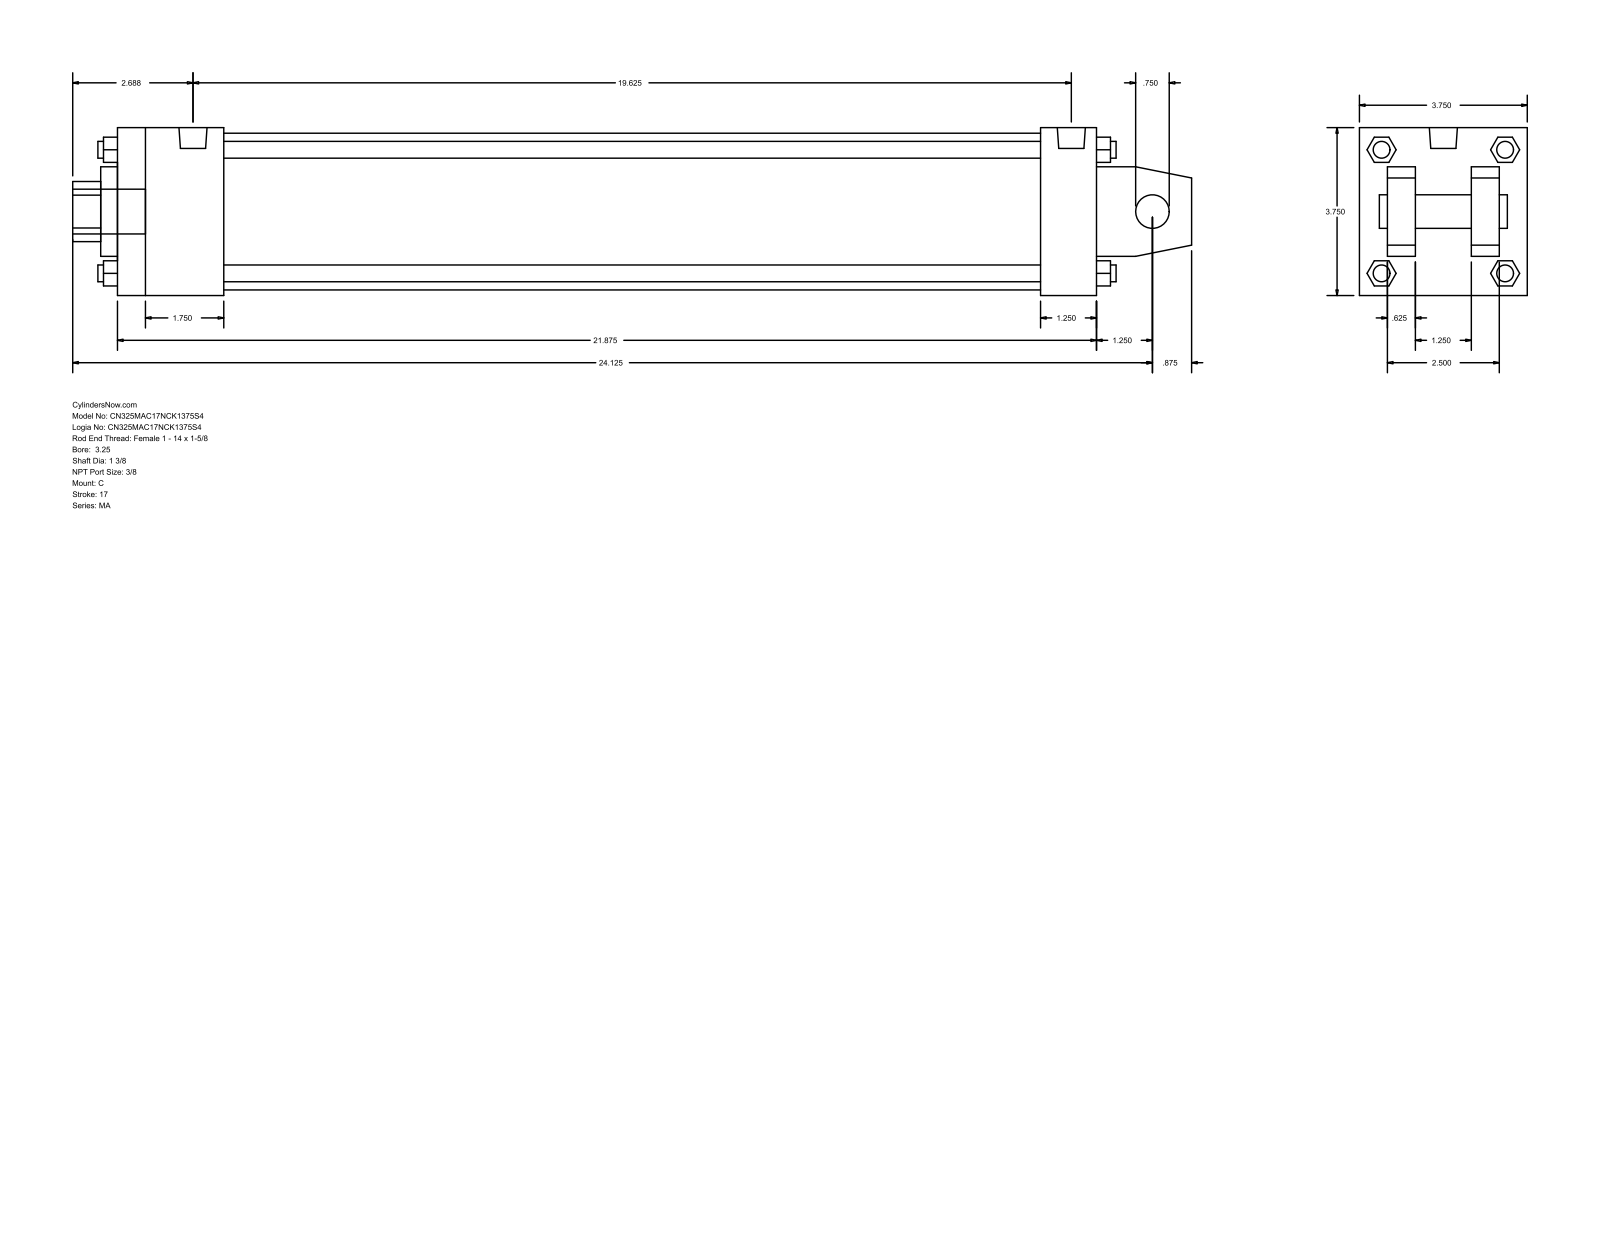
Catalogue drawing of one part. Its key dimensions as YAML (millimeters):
part_name: "MA_C__0325_1.375"
step_written_by: "GSSL Pune (CONFIG_CONTROL_DESIGN)"
units: millimeters
bodies: {solids: 0, faces: 139, planar: 108, cylindrical: 31, other: 0}
overall_size: [635, 95.25, 95.25]
round_holes:
  - {diameter: 19.05, count: 1}
  - {diameter: 34.92, count: 1}
  - {diameter: 50.8, count: 1}
  - {diameter: 88.9, count: 1}
round_bosses_or_shafts:
  - {diameter: 11.11, count: 4}
  - {diameter: 9.53, count: 4}
  - {diameter: 15.93, count: 2}
  - {diameter: 25.4, count: 1}
partial_cylinders:
  - {radius: 17.06, count: 1}
face_to_face_distances: [95.24, 15.87, 63.5, 555.62, 31.74, 79.37, 47.63, 523.87, 31.75, 60.32]
